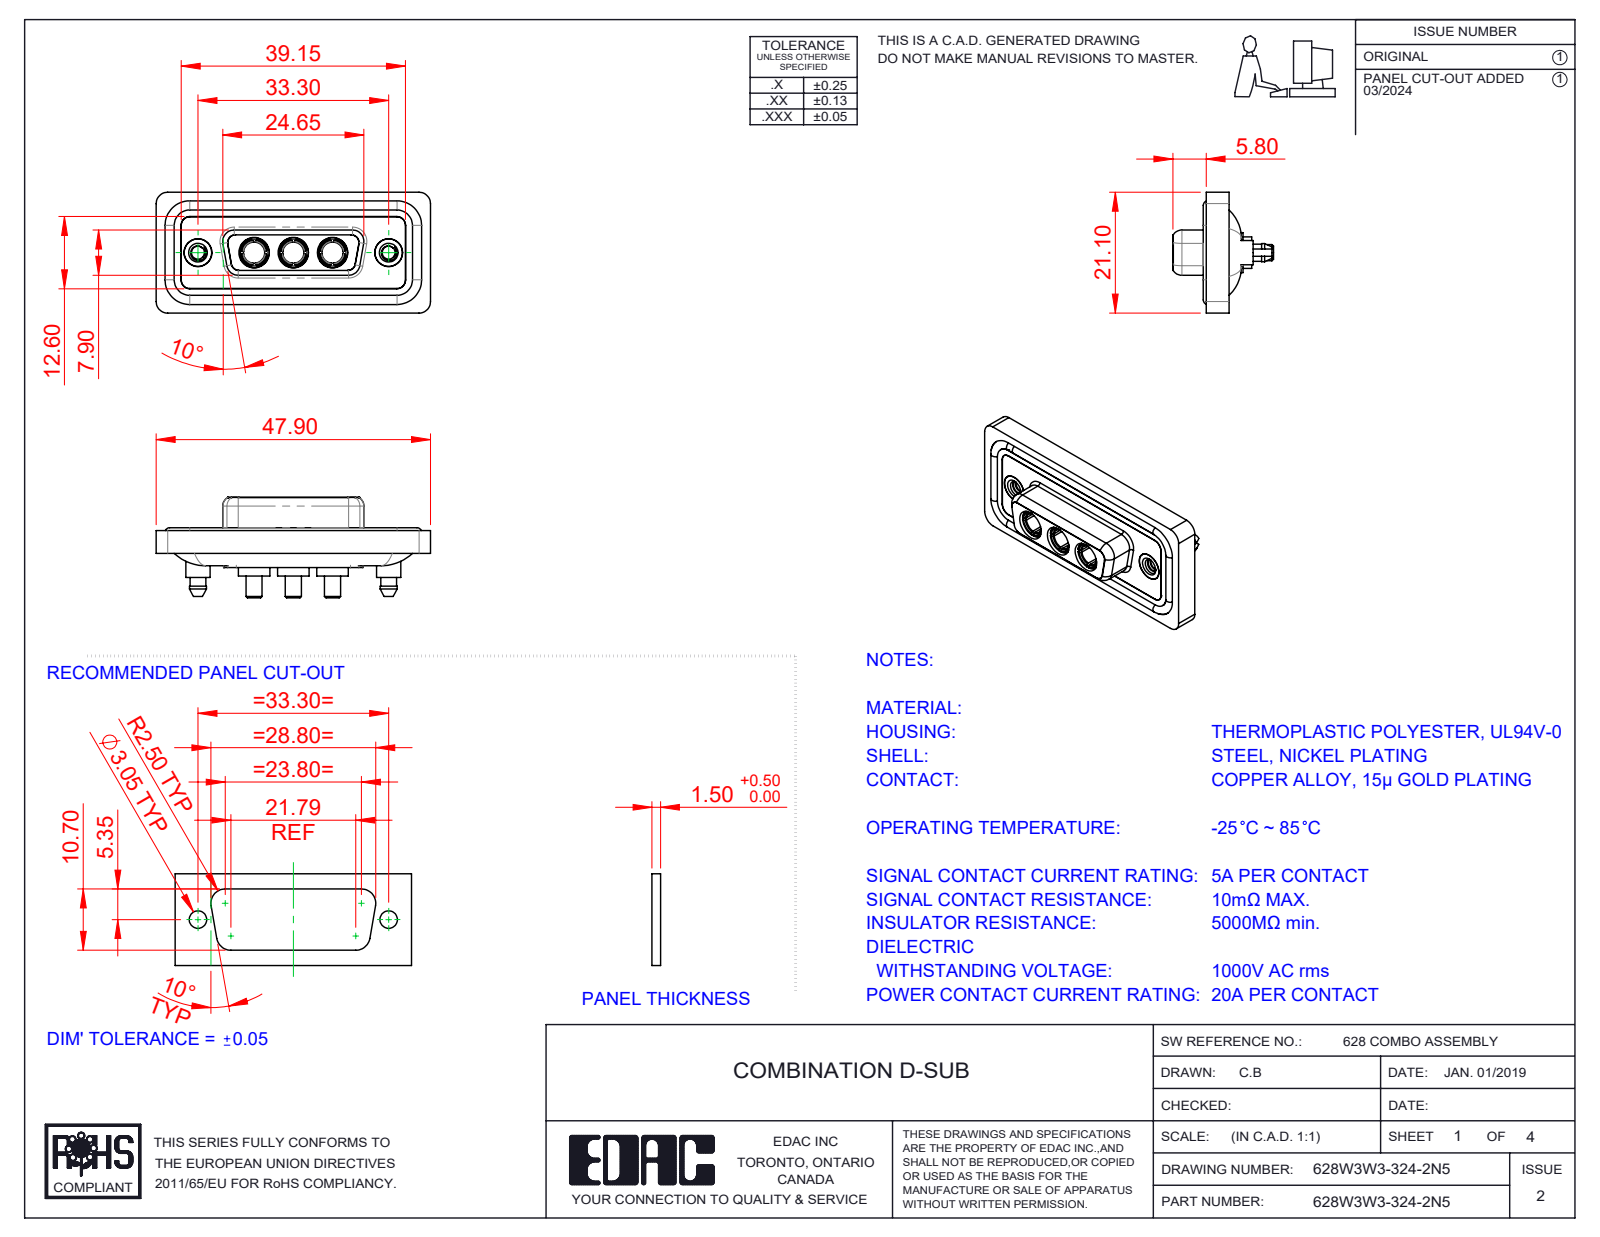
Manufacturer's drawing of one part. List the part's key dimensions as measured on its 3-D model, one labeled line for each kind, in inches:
Part name (STEP PRODUCT): 628Combo Threaded Boardlock_5; 628Combo Waterproof Housing_15 Contacts; 628Combo Housing_3W3; Power Socket_20A S (+3 more)
STEP written by: SolidWorks 2023 (CONFIG_CONTROL_DESIGN)
Units: inches
Bodies: 13 solids, 658 faces (208 planar, 289 cylindrical, 161 other)
Overall size (bounding box): 1.886 × 0.831 × 0.691
Volume: 0.376 in³ · Surface area: 15.61 in²
Round holes (diameter × count): ⌀0.191 ×5, ⌀0.146 ×3, ⌀0.209 ×3, ⌀0.089 ×2, ⌀0.157 ×2, ⌀0.159 ×2, ⌀0.197 ×2
Round bosses / shafts (diameter × count): ⌀0.063 ×4, ⌀0.217 ×3, ⌀0.205 ×3, ⌀0.195 ×3, ⌀0.187 ×3, ⌀0.148 ×3, ⌀0.11 ×3, ⌀0.213 ×2
Partial cylindrical surfaces — rounded edges, fillets, slot ends (radius × count): R0.059 ×24, R0.079 ×20, R0.053 ×12, R0.063 ×10, R0.01 ×4, R0.02 ×4, R0.024 ×4, R0.026 ×4
Main face-to-face distances: 0.016, 0.071, 0.063, 0.02, 0.293, 0.043, 0.114, 0.222, 0.278, 0.26
Hole centre spacings: 0.27, 0.386, 0.656, 0.925, 0.539, 1.311
